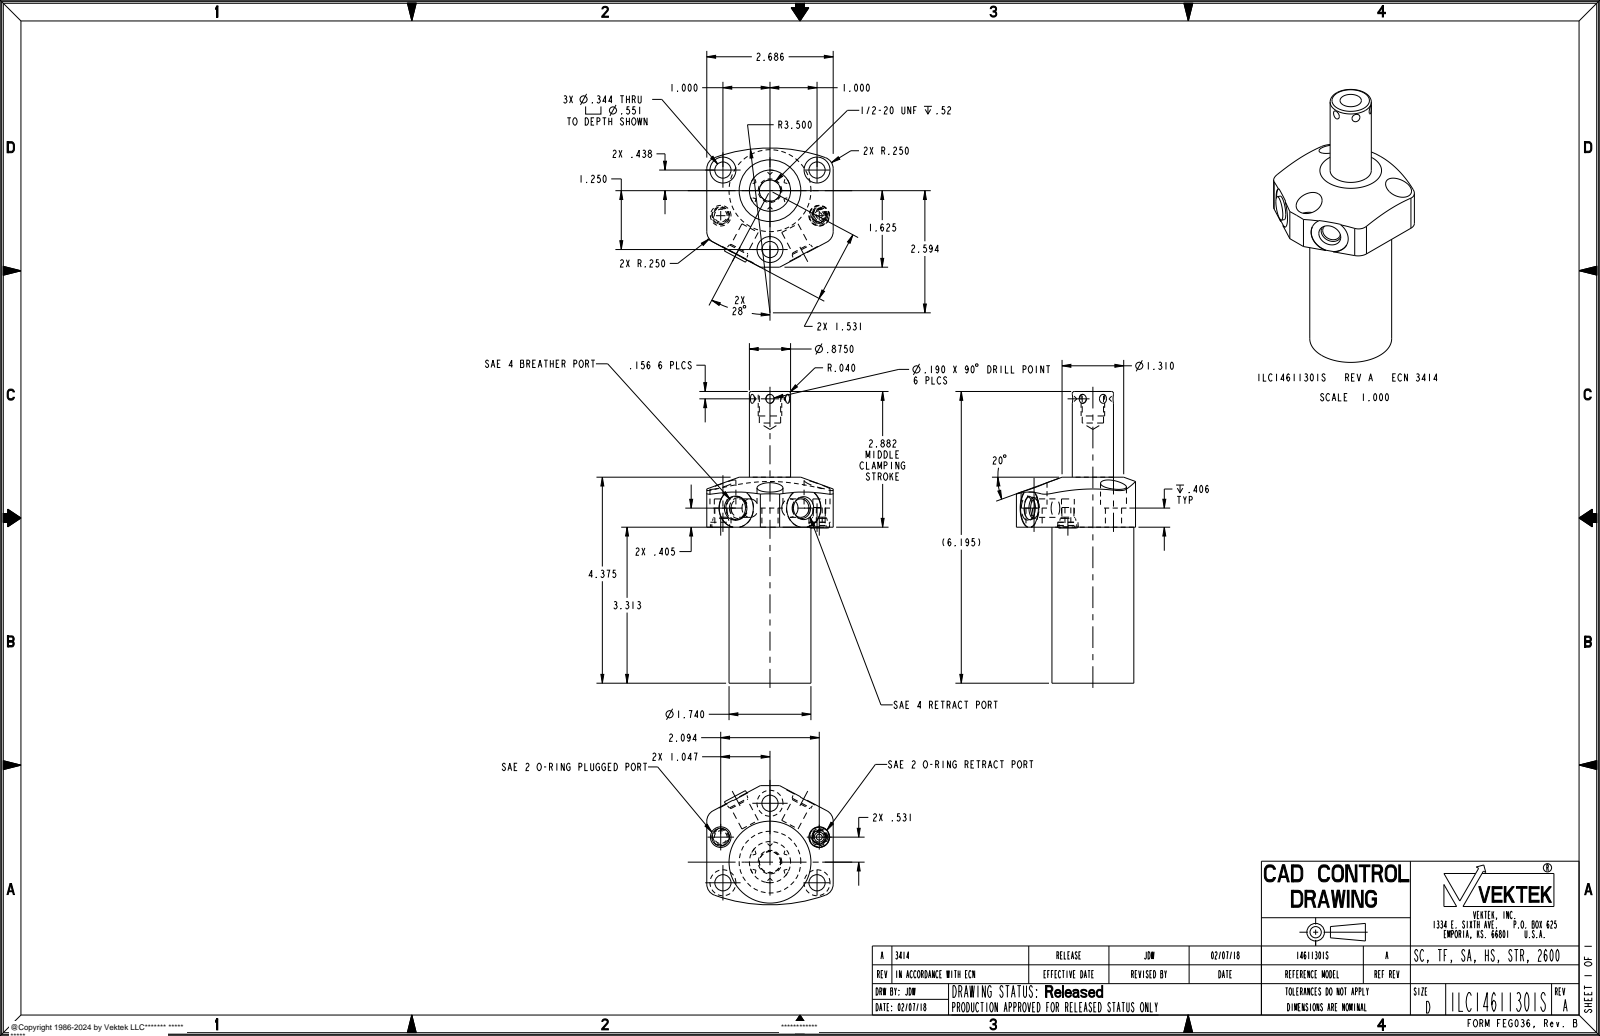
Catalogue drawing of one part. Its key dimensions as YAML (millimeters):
part_name: "ILC14611301S"
step_written_by: "PRO/ENGINEER BY PARAMETRIC TECHNOLOGY CORPORATION, 2013320 (AUTOMOTIVE_DESIGN)"
units: millimeters
bodies: {solids: 1, faces: 123, planar: 32, cylindrical: 53, other: 38}
overall_size: [157.4, 68.2, 64.3]
volume: 224000
surface_area: 33200
round_holes:
  - {diameter: 8.7, count: 3}
  - {diameter: 14, count: 3}
  - {diameter: 6.9, count: 2}
  - {diameter: 10, count: 2}
  - {diameter: 11.1, count: 2}
  - {diameter: 3.2, count: 1}
  - {diameter: 11.5, count: 1}
round_bosses_or_shafts:
  - {diameter: 44.2, count: 1}
  - {diameter: 22.2, count: 1}
  - {diameter: 12.9, count: 1}
  - {diameter: 12.7, count: 1}
  - {diameter: 10.9, count: 1}
  - {diameter: 9.6, count: 1}
  - {diameter: 6.5, count: 1}
  - {diameter: 5.3, count: 1}
partial_cylinders:
  - {radius: 6.4, count: 4}
  - {radius: 10.5, count: 2}
  - {radius: 88.9, count: 1}
face_to_face_distances: [84.2, 68.2, 111.1, 27, 94.5, 10.3, 16.7, 157.4, 73.2, 62.9]
hole_center_spacings: [24.6, 27.7, 29.8, 32.3, 49.8, 57.5, 31.8, 50.8]
